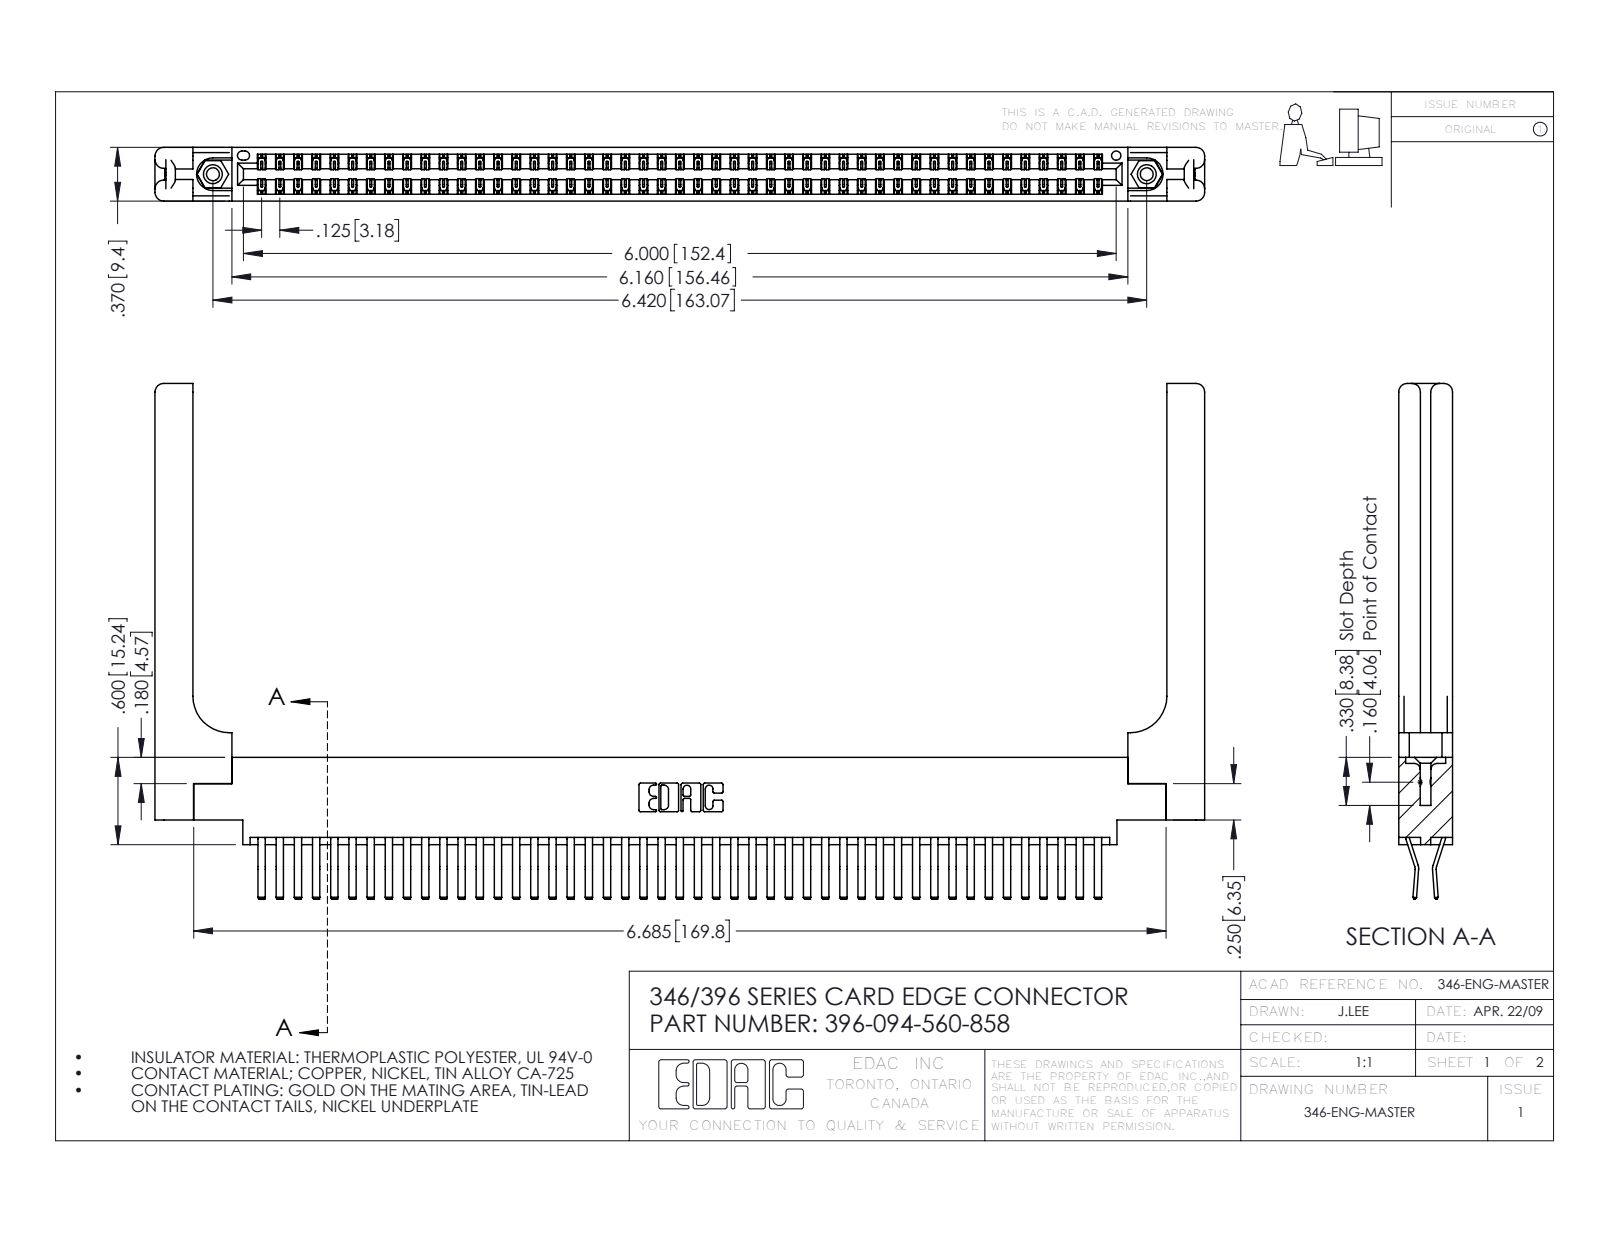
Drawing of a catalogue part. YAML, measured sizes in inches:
part_name: "346-220-058_345-220-058; 396-094-560-858; 345-250-001_345-250-001-102; 345-292-001_560 Tail (+1 more)"
step_written_by: "SolidWorks 2016 (CONFIG_CONTROL_DESIGN)"
units: inches
bodies: {solids: 99, faces: 5458, planar: 3518, cylindrical: 1880, other: 60}
overall_size: [7.216, 3.545, 0.37]
volume: 1.579
surface_area: 49.8
round_holes:
  - {diameter: 0.089, count: 2}
  - {diameter: 0.125, count: 2}
  - {diameter: 0.156, count: 2}
  - {diameter: 0.064, count: 1}
round_bosses_or_shafts:
  - {diameter: 0.155, count: 2}
partial_cylinders:
  - {radius: 0.006, count: 141}
  - {radius: 0.01, count: 22}
  - {radius: 0.06, count: 16}
  - {radius: 0.007, count: 6}
  - {radius: 0.031, count: 6}
  - {radius: 0.026, count: 3}
  - {radius: 0.01, count: 2}
  - {radius: 0.014, count: 2}
face_to_face_distances: [0.37, 0.048, 0.322, 0.072, 0.025, 0.148, 0.15, 0.25, 0.298, 0.275]
hole_center_spacings: [0.246, 6.211, 6.42]
